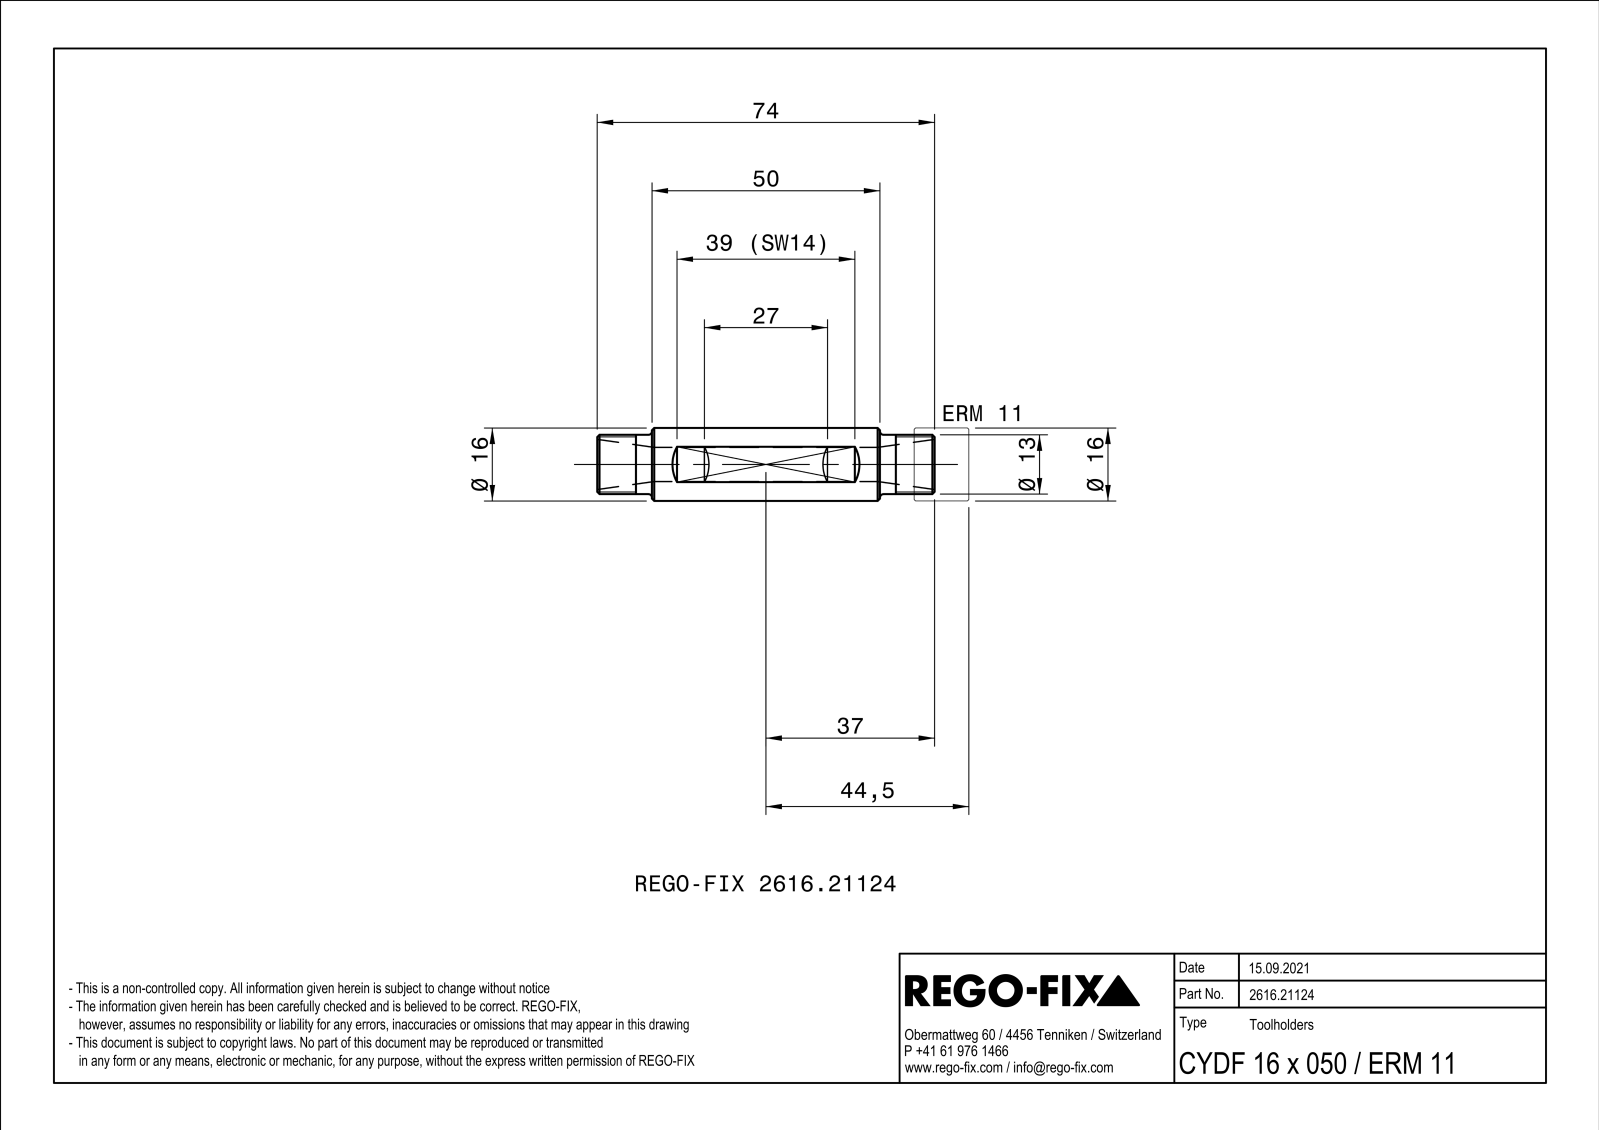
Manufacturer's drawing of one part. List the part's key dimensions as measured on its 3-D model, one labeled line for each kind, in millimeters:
Part name (STEP PRODUCT): NOCUT
STEP written by: SIEMENS PLM Software Solid Edge ST10 (AUTOMOTIVE_DESIGN)
Units: millimetres
Bodies: 1 solid, 29 faces (13 planar, 6 cylindrical, 10 other)
Overall size (bounding box): 74 × 16 × 16
Volume: 9 085 mm³ · Surface area: 5 500 mm²
Round holes (diameter × count): ⌀7.5 ×1
Round bosses / shafts (diameter × count): ⌀16 ×1, ⌀13 ×1
Main face-to-face distances: 14, 12, 62, 17.68, 5.65, 23.33, 74, 50
